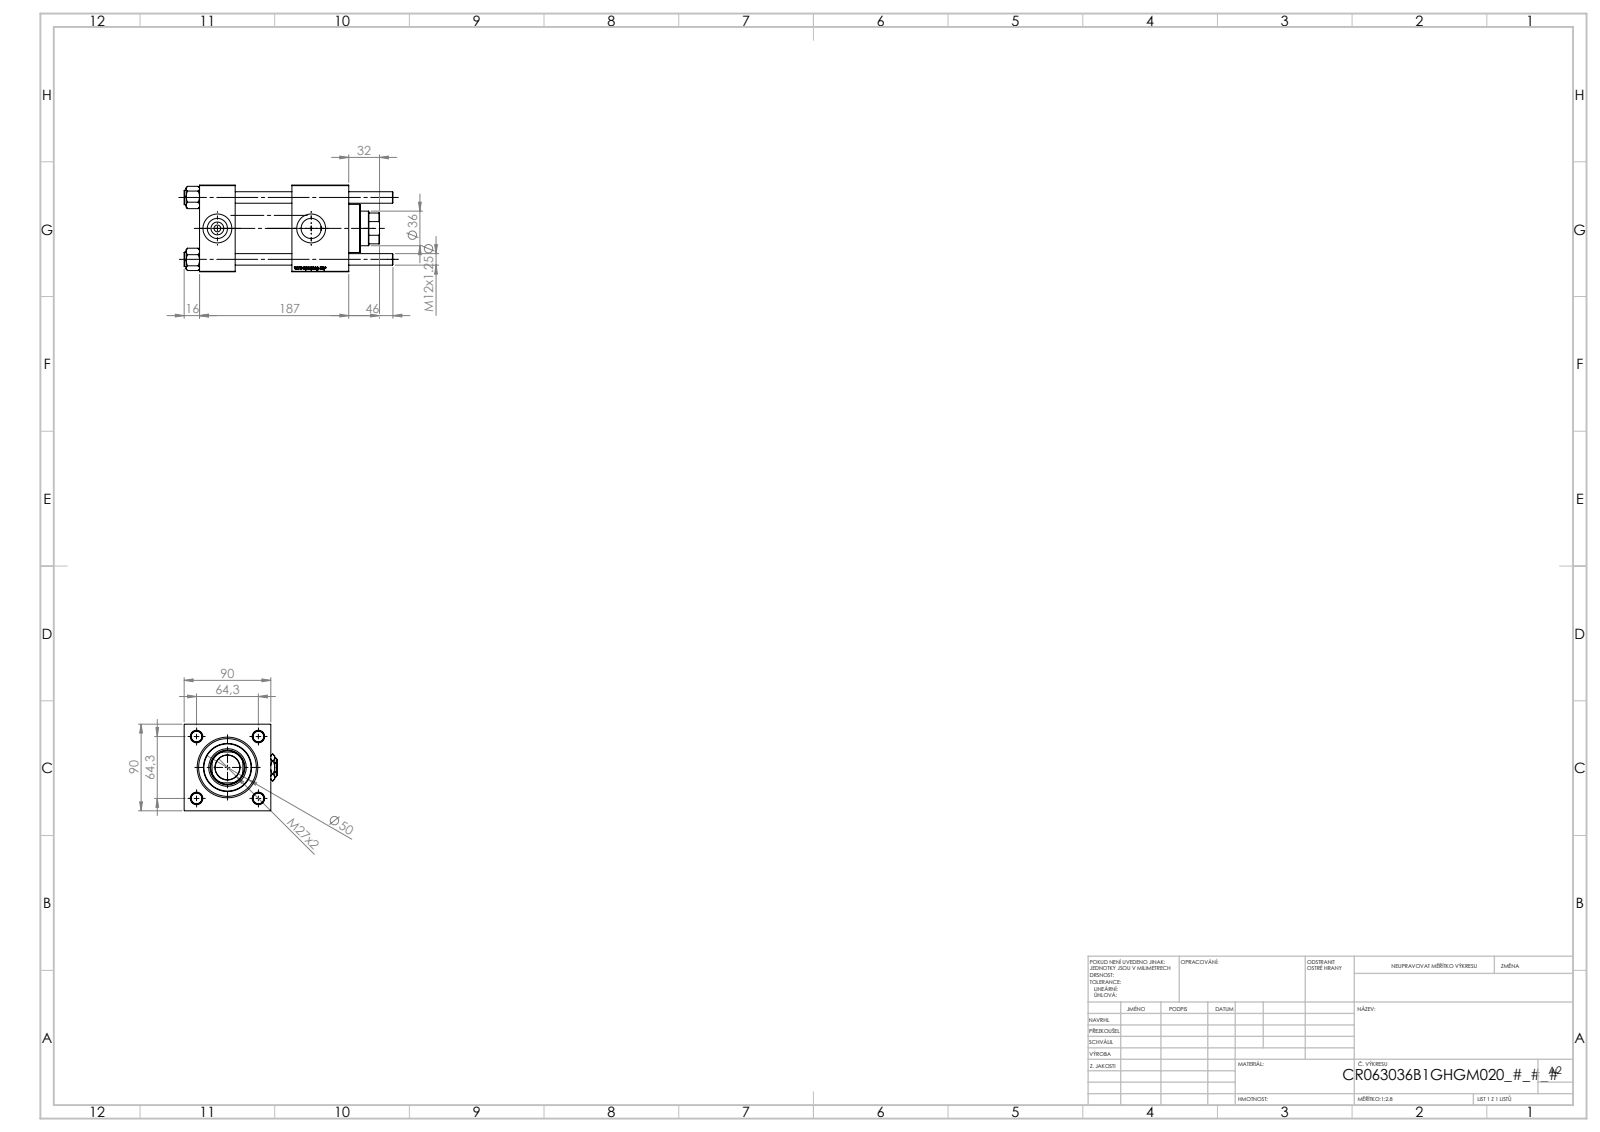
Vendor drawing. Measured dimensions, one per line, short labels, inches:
name: V215CR_B-1; V215CR_B_TYCINKA; NUT_M5_B; V215_VC_A (+2 more)
written by: SolidWorks 2019 (CONFIG_CONTROL_DESIGN)
unit: in
bodies: 12 solids, 1205 faces (455 planar, 82 cylindrical, 668 other)
size: 8.543 × 3.819 × 3.543
volume: 60.9 in³; area: 313.5 in²
holes: 4× ⌀0.472, 2× ⌀0.276, 2× ⌀0.825, 2× ⌀1.181, 1× ⌀1.004, 1× ⌀1.417, 1× ⌀1.535, 1× ⌀1.969, 1× ⌀2.362, 1× ⌀2.48
bosses: 4× ⌀0.591, 1× ⌀2.717
rounds: 1× R0.689
face distances: 3.543, 2.323, 1.457, 4.646, 6.102, 3.78, 4.972, 3.516, 1.193, 1.13
hole spacings: 1.79, 2.531, 3.58, 3.839
